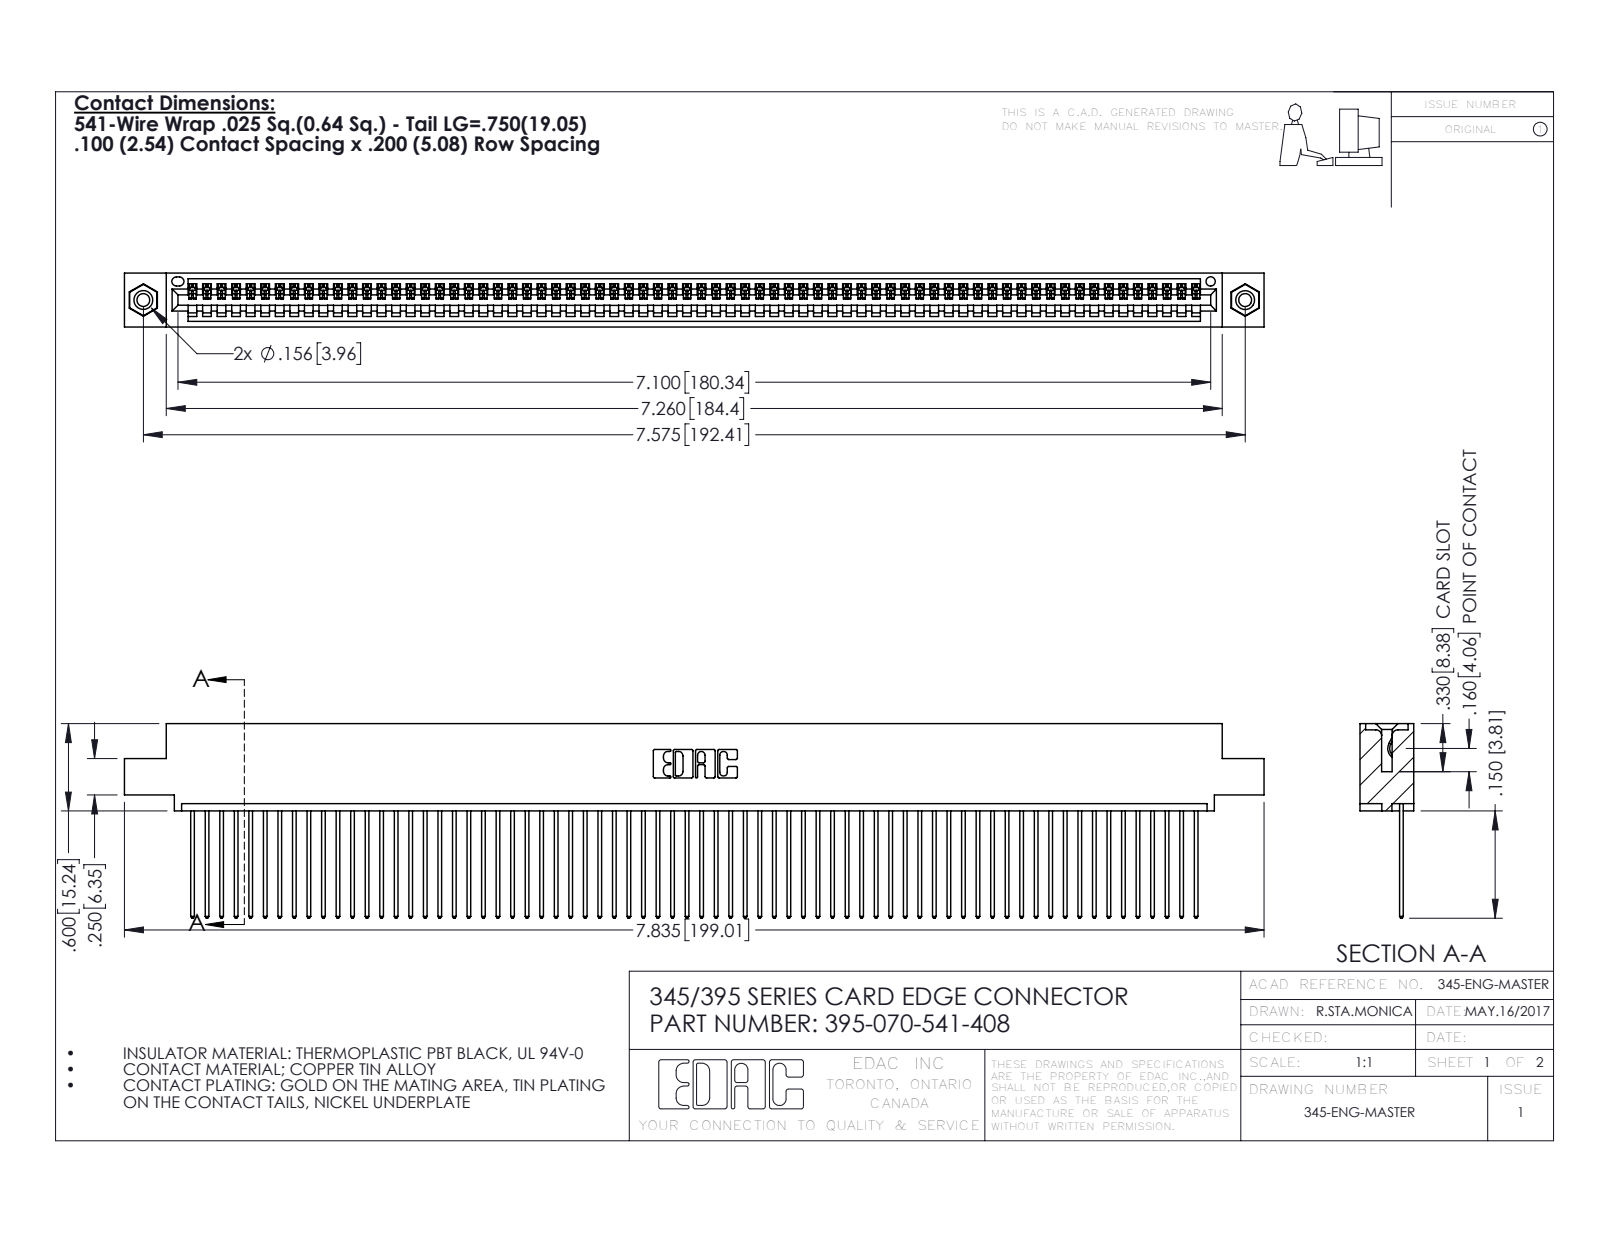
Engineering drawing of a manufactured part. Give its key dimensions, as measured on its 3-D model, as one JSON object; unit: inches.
{"part_name": "345-250-001_345-250-003-102; 345 Part_0.110 Offset - 0.156 Dia-TI; 345-292-001_345-293-141; 395-070-541-408", "step_written_by": "SolidWorks 2016 (CONFIG_CONTROL_DESIGN)", "units": "inches", "bodies": {"solids": 73, "faces": 4250, "planar": 2916, "cylindrical": 1318, "other": 16}, "overall_size": [7.835, 1.337, 0.37], "volume_in3": 1.177, "surface_area_in2": 42.57, "round_holes": [[0.089, 2], [0.125, 2], [0.156, 2], [0.064, 1]], "round_bosses_or_shafts": [[0.155, 2]], "partial_cylinders_radius": [[0.006, 140], [0.01, 140], [0.01, 22], [0.007, 6], [0.031, 6], [0.026, 3], [0.031, 2], [0.04, 2]], "face_to_face_distances": [0.072, 0.298, 0.098, 0.272, 0.025, 0.37, 0.2, 0.225, 0.149, 0.072], "hole_center_spacings": [0.27, 7.339, 7.575]}
